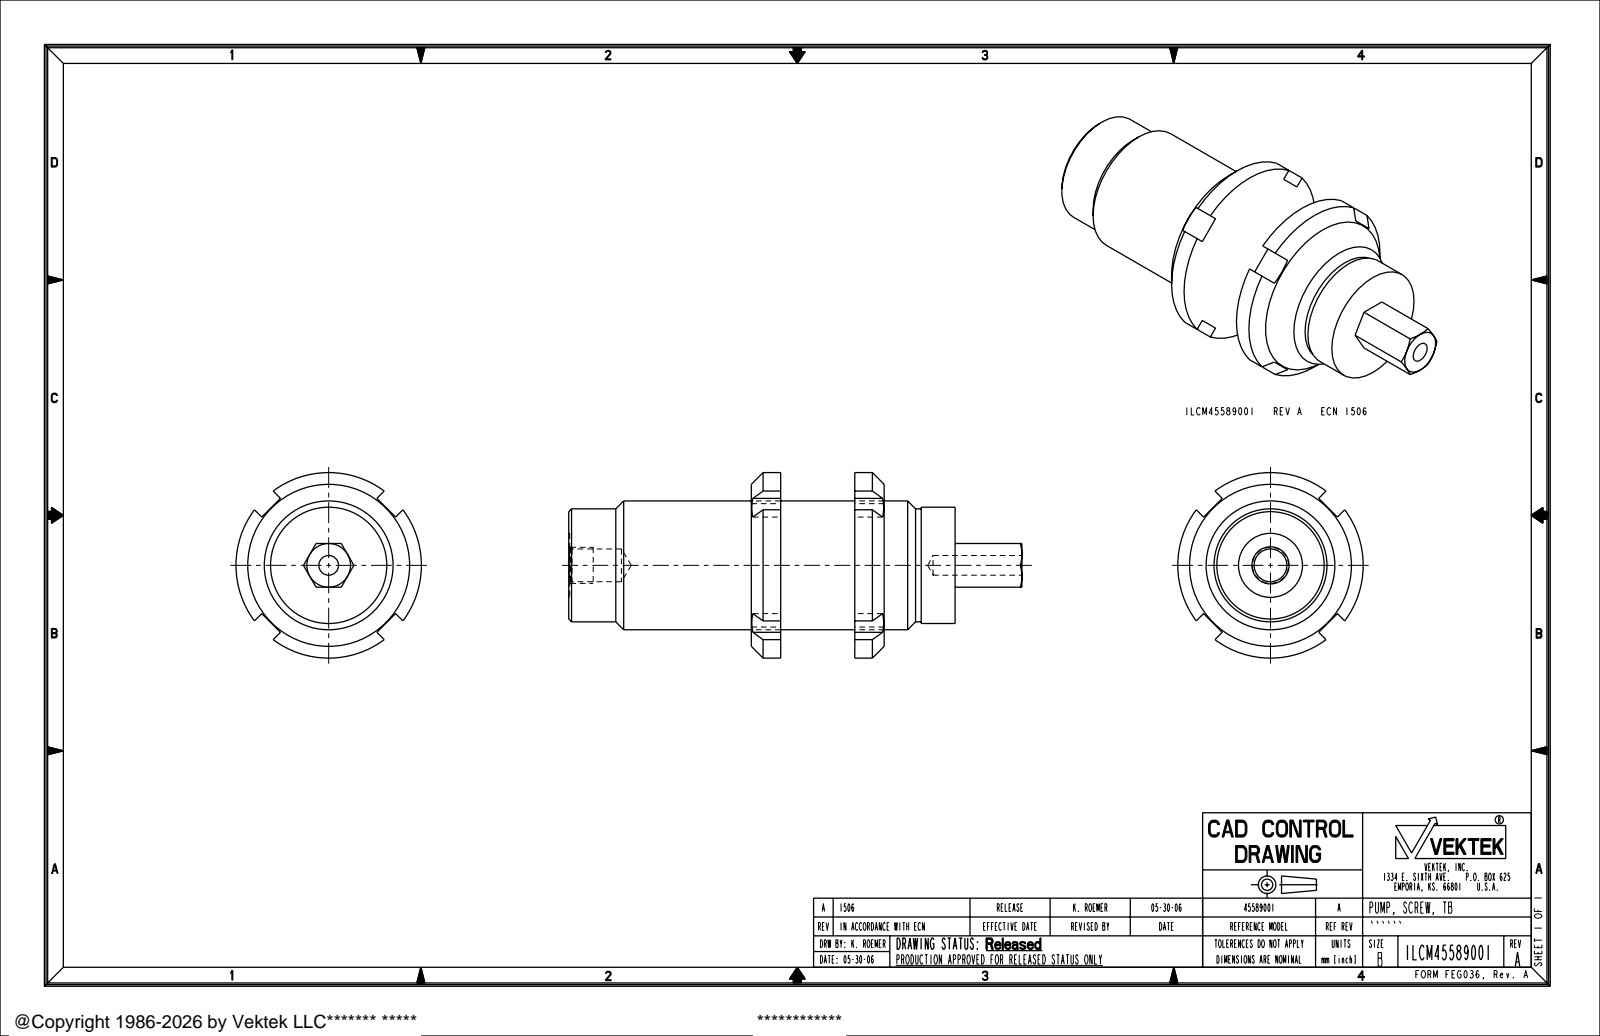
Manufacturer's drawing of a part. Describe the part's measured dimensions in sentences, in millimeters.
The part is named "ILCM45589001; ILCM45589001_NUT; ILCM45589001_ASM". Its 3-D file was written by "PRO/ENGINEER BY PARAMETRIC TECHNOLOGY CORPORATION, 2004290 (AUTOMOTIVE_DESIGN_CC2)". It is 3 solids with 92 faces: 40 planar, 30 cylindrical and 22 other. Overall it measures 122.3 by 50.04 by 50.04 millimeters. Its volume is 109 120 cubic millimeters and its surface area 22 446 square millimeters. Round holes: 1 of diameter 5.31, 1 of diameter 8.84, 1 of diameter 10.03, 1 of diameter 17.27, 1 of diameter 33.27. Round bosses or shafts: 1 of diameter 50.04, 1 of diameter 34.75, 1 of diameter 31.37, 1 of diameter 30.48, 1 of diameter 9.73. The main face-to-face distances are 20, 47.06, 27.06, 7.93, 27.93, 35.85, 54.99, 27.92, 7.92, 19.14.
